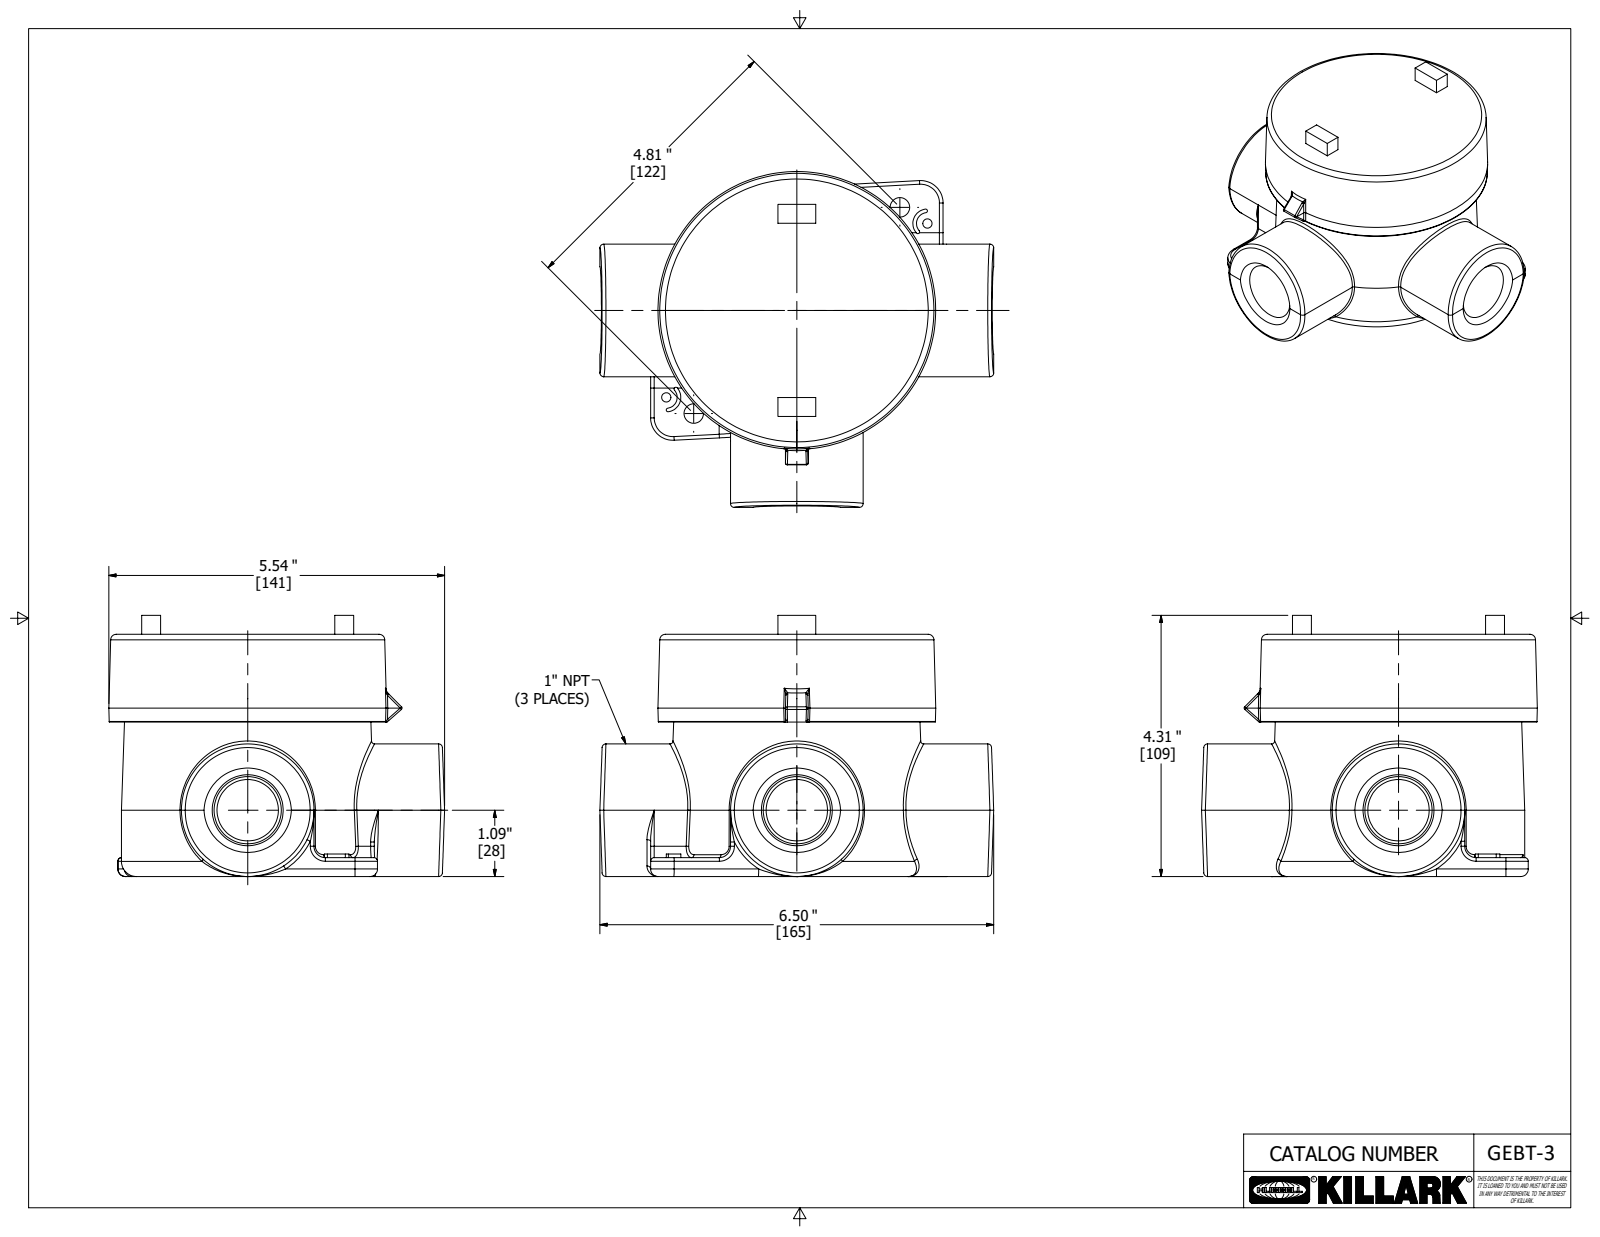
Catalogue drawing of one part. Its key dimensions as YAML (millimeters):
part_name: "GEBT-3; 21156; 21147-override"
step_written_by: "Autodesk Inventor 2020 (AUTOMOTIVE_DESIGN)"
units: millimeters
bodies: {solids: 2, faces: 863, planar: 410, cylindrical: 95, other: 358}
overall_size: [165.1, 140.8, 109.5]
volume: 652000
surface_area: 137700
round_holes:
  - {diameter: 3.9, count: 2}
  - {diameter: 8.2, count: 2}
  - {diameter: 25.7, count: 2}
  - {diameter: 39.6, count: 2}
  - {diameter: 97.1, count: 1}
  - {diameter: 102.7, count: 1}
round_bosses_or_shafts:
  - {diameter: 55.6, count: 2}
partial_cylinders:
  - {radius: 1.5, count: 34}
  - {radius: 0.8, count: 14}
  - {radius: 3.2, count: 4}
  - {radius: 0.8, count: 3}
  - {radius: 4.7, count: 3}
  - {radius: 4.6, count: 2}
  - {radius: 6.1, count: 2}
  - {radius: 9.4, count: 2}
face_to_face_distances: [101.5, 90.4, 11.1, 64.7, 25.7, 36.8, 88.9, 9.7, 55.1, 80.8]
hole_center_spacings: [13.4, 126.2, 61.1, 61.1, 65.8, 65.8, 122.2, 131.5]
